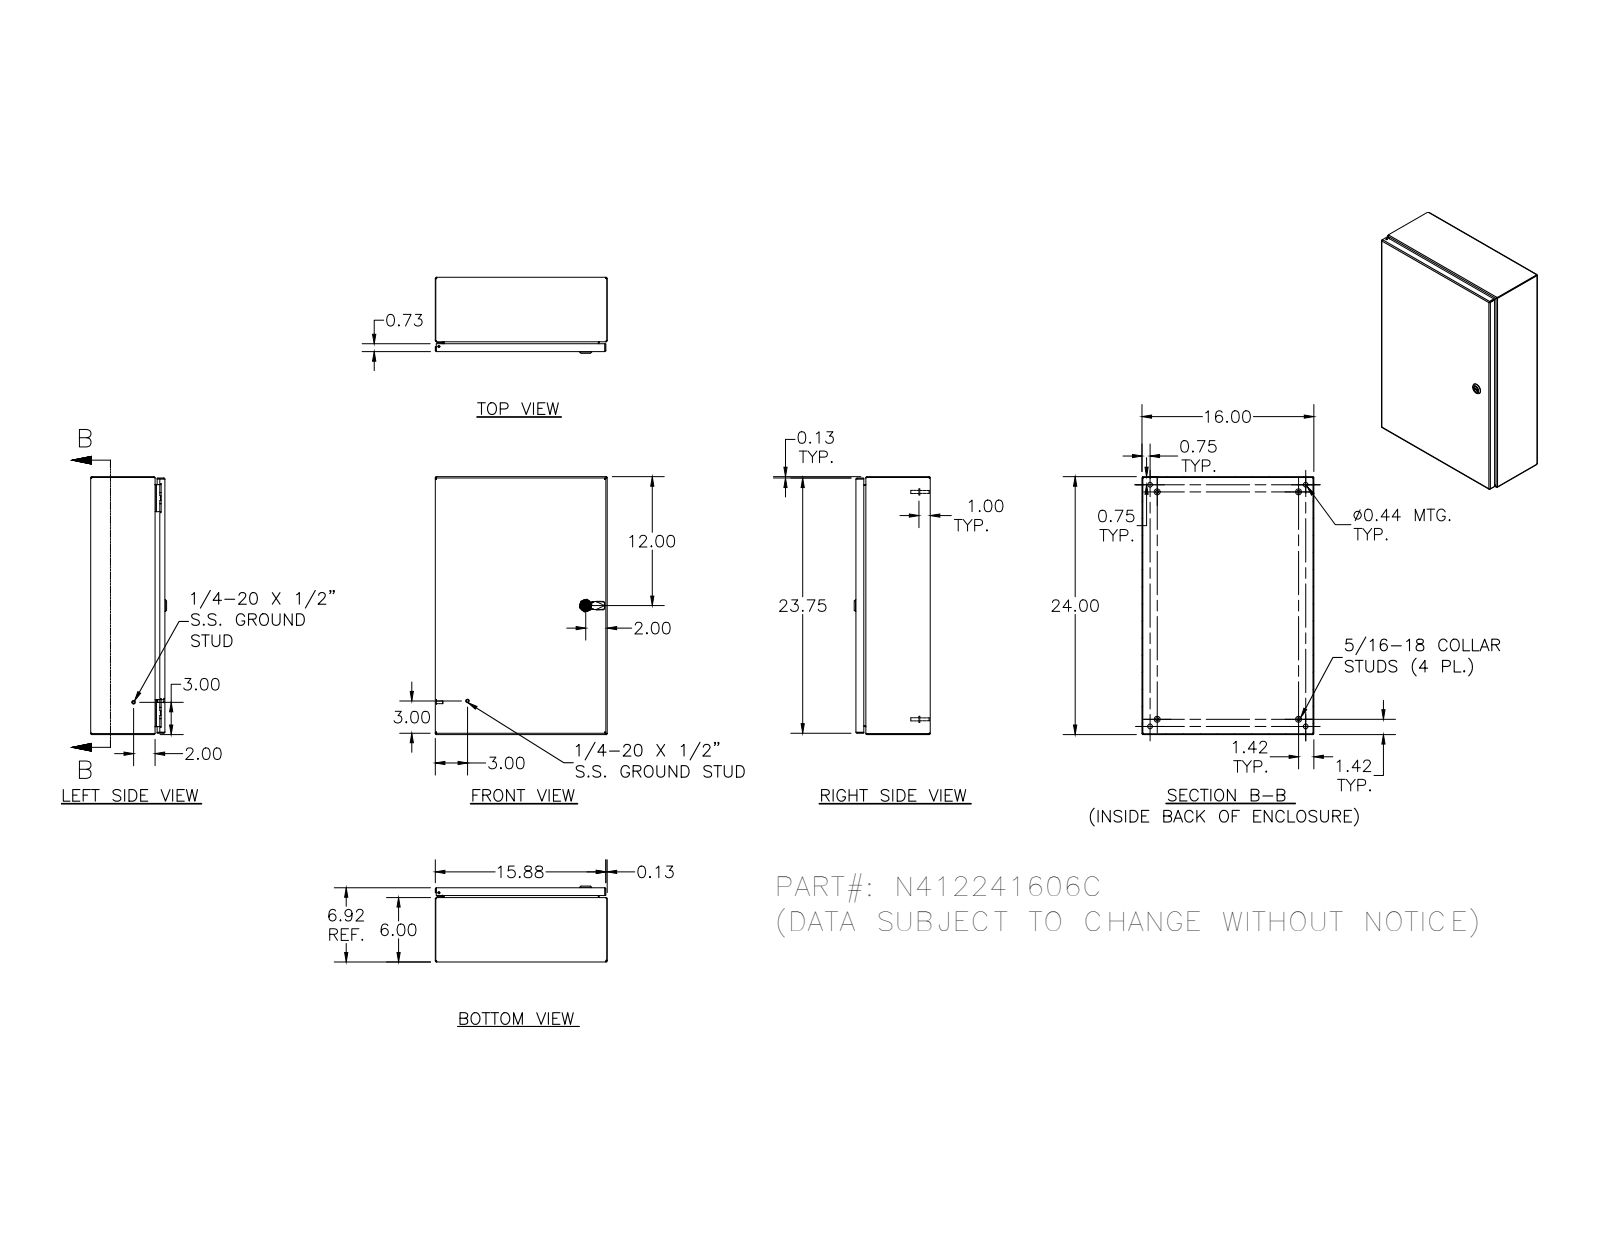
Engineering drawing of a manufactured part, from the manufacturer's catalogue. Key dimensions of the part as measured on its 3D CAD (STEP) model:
Part name (STEP PRODUCT): N412241606C
STEP written by: SolidWorks 2018 (AUTOMOTIVE_DESIGN)
Units: inches
Bodies: 33 solids, 1449 faces (530 planar, 547 cylindrical, 372 other)
Overall size (bounding box): 24 × 16 × 7.075
Volume: 104.4 in³ · Surface area: 2 841 in²
Round holes (diameter × count): ⌀0.188 ×5, ⌀0.093 ×4, ⌀0.152 ×4, ⌀0.167 ×4, ⌀0.172 ×4, ⌀0.437 ×4, ⌀0.156 ×2, ⌀0.187 ×1, ⌀0.197 ×1, ⌀0.315 ×1, ⌀0.394 ×1, ⌀0.402 ×1
Round bosses / shafts (diameter × count): ⌀0.25 ×10, ⌀0.563 ×4, ⌀0.36 ×4, ⌀0.32 ×4, ⌀0.3 ×4, ⌀0.256 ×4, ⌀0.164 ×4, ⌀0.131 ×4
Partial cylindrical surfaces — rounded edges, fillets, slot ends (radius × count): R0.012 ×30, R0.031 ×30, R0.05 ×26, R0.105 ×20, R0.016 ×18, R0.125 ×16, R0.02 ×13, R0.032 ×8
Main face-to-face distances: 0.074, 6.843, 6.769, 6.917, 0.074, 15.926, 16, 15.852, 15.926, 0.917
Hole centre spacings: 20, 0.66, 0.656, 1.307, 1.965, 0.5, 0.984, 1.311
